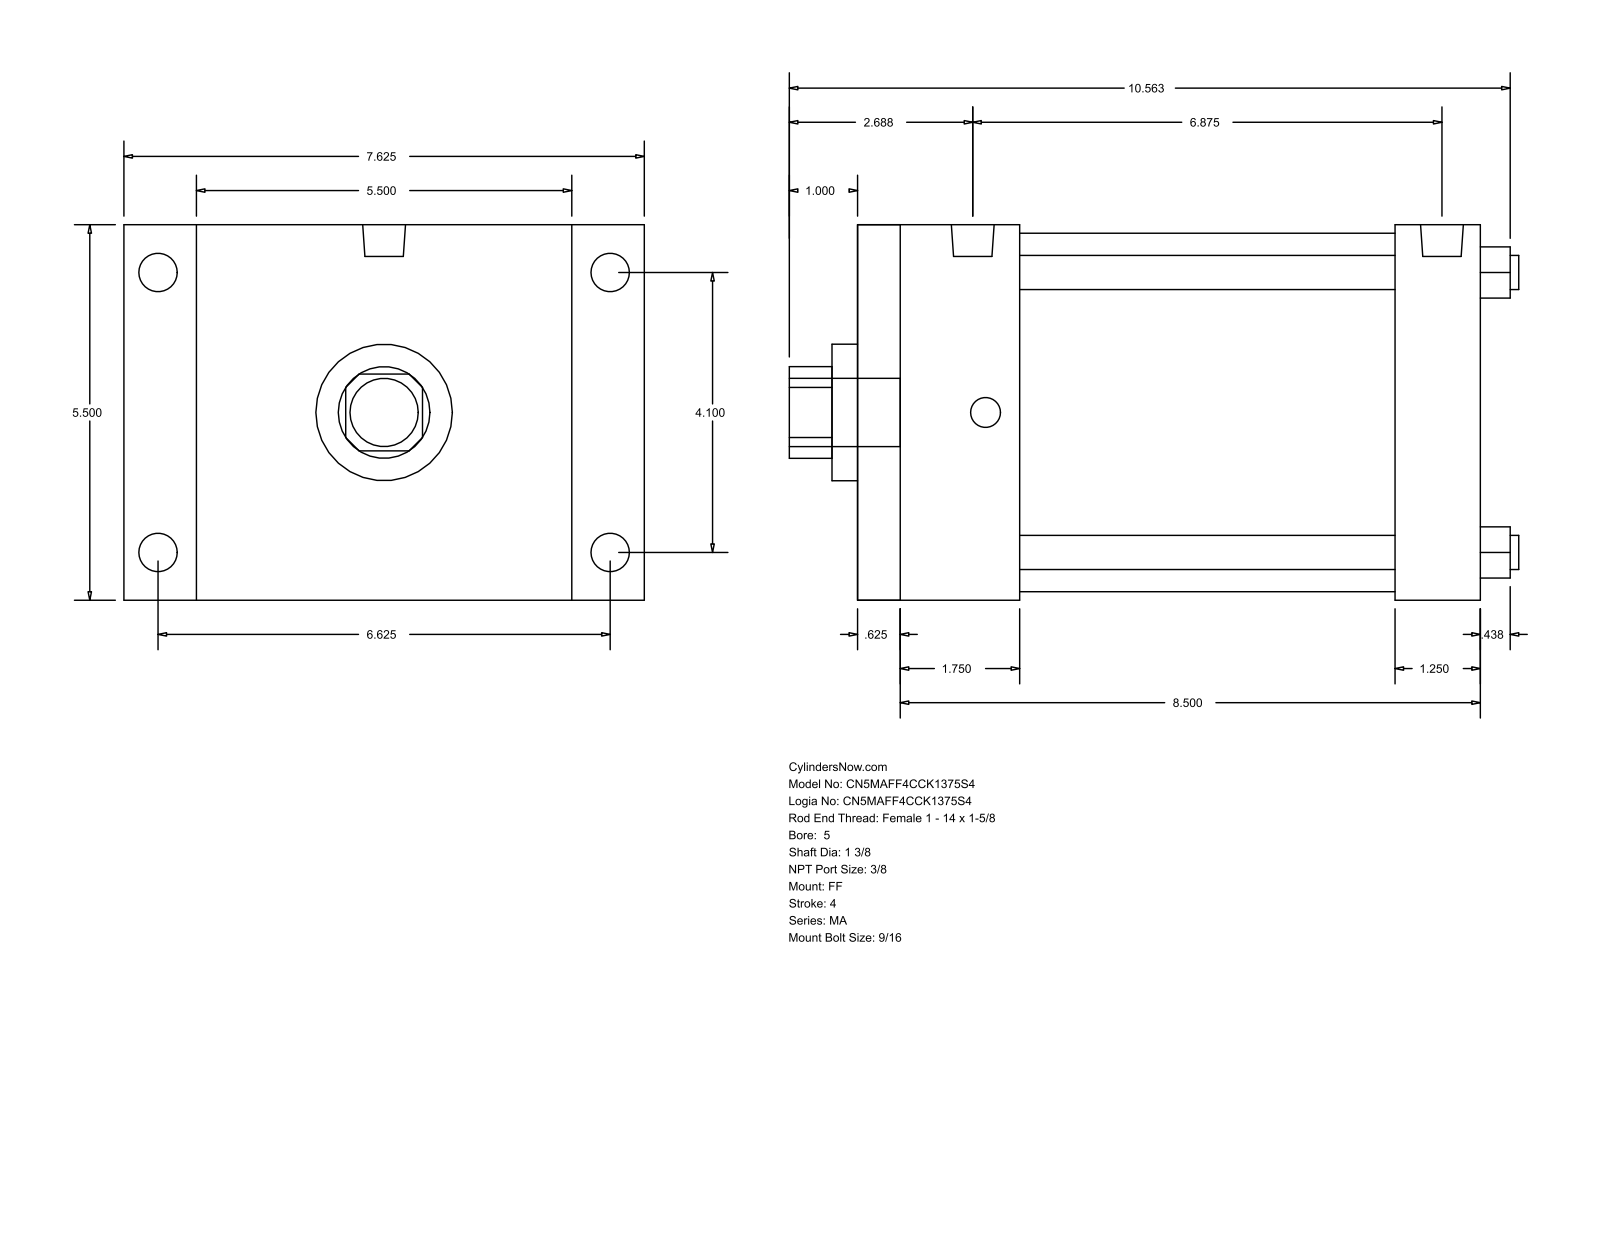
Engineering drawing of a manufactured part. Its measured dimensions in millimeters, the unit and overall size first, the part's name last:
Units: millimetres
Overall size (bounding box): 271.46 × 193.68 × 139.7
Round holes (diameter × count): ⌀12.7 ×4, ⌀34.92 ×1, ⌀50.8 ×1, ⌀133.35 ×1
Round bosses / shafts (diameter × count): ⌀14.29 ×4, ⌀11.11 ×4, ⌀15.93 ×2, ⌀25.4 ×1
Partial cylindrical surfaces — rounded edges, fillets, slot ends (radius × count): R17.06 ×1
Main face-to-face distances: 139.7, 231.78, 15.87, 215.91, 200.03, 184.16, 31.75, 60.32, 44.45, 139.71
Hole centre spacings: 73.64, 104.14, 147.28
Bodies: 0 solids, 92 faces (64 planar, 28 cylindrical, 0 other)
Part name (STEP PRODUCT): MA_FF__0500_1.375
STEP written by: GSSL Pune (CONFIG_CONTROL_DESIGN)
